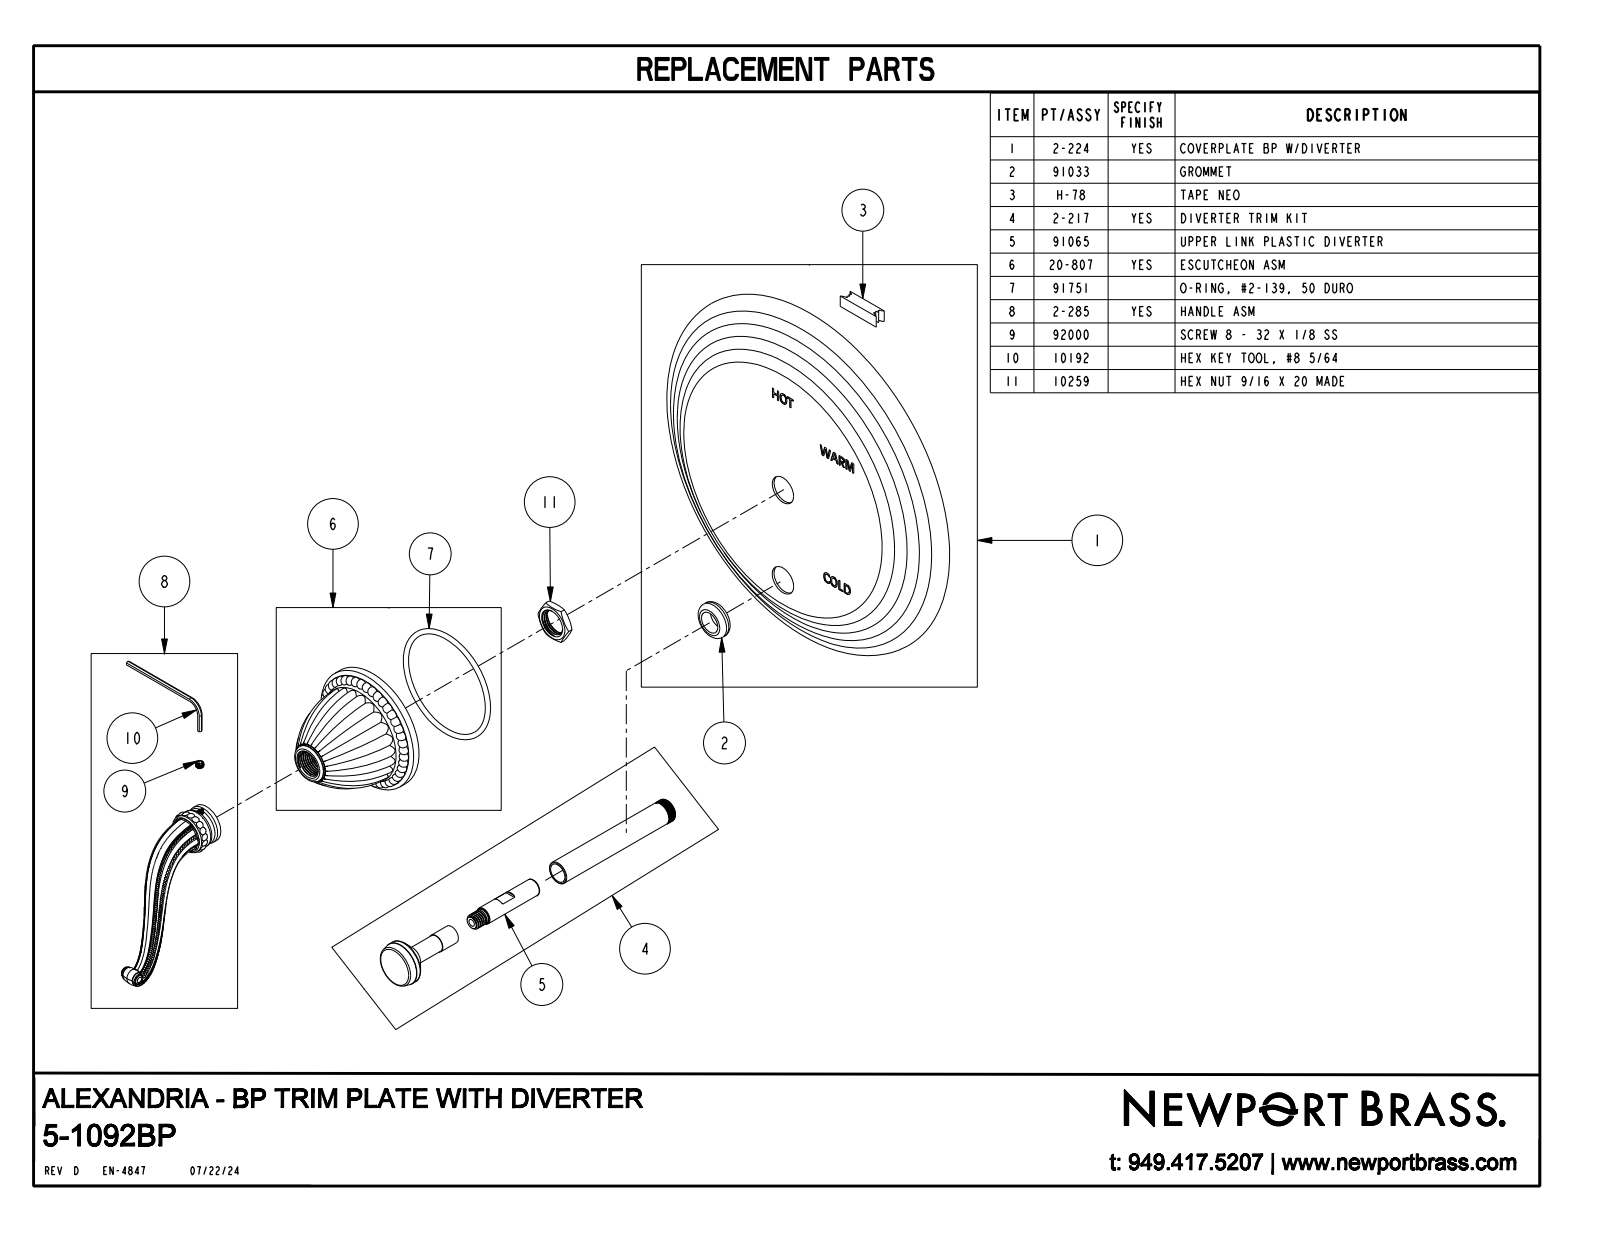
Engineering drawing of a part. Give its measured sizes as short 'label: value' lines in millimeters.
name: 5-1092BP
written by: CREO PARAMETRIC BY PTC INC, 2018400 (CONFIG_CONTROL_DESIGN)
unit: mm
bodies: 1 solid, 3305 faces (432 planar, 1106 cylindrical, 1767 other)
size: 196.9 × 196.9 × 122.1
volume: 547 800 mm³; area: 80 900 mm²
holes: 189× ⌀1, 49× ⌀1.3, 23× ⌀1.1, 11× ⌀1
bosses: 1× ⌀65.3, 1× ⌀22.9, 1× ⌀20.1, 1× ⌀19.7, 1× ⌀12, 1× ⌀10.2, 1× ⌀9
face distances: 19.2, 58.1, 38.9, 65.9, 46.7, 7.8, 65.1, 46, 7.1, 0.8
hole spacings: 1.3, 1.3, 1.4, 1.4, 2.6, 3.9, 4, 4.8
